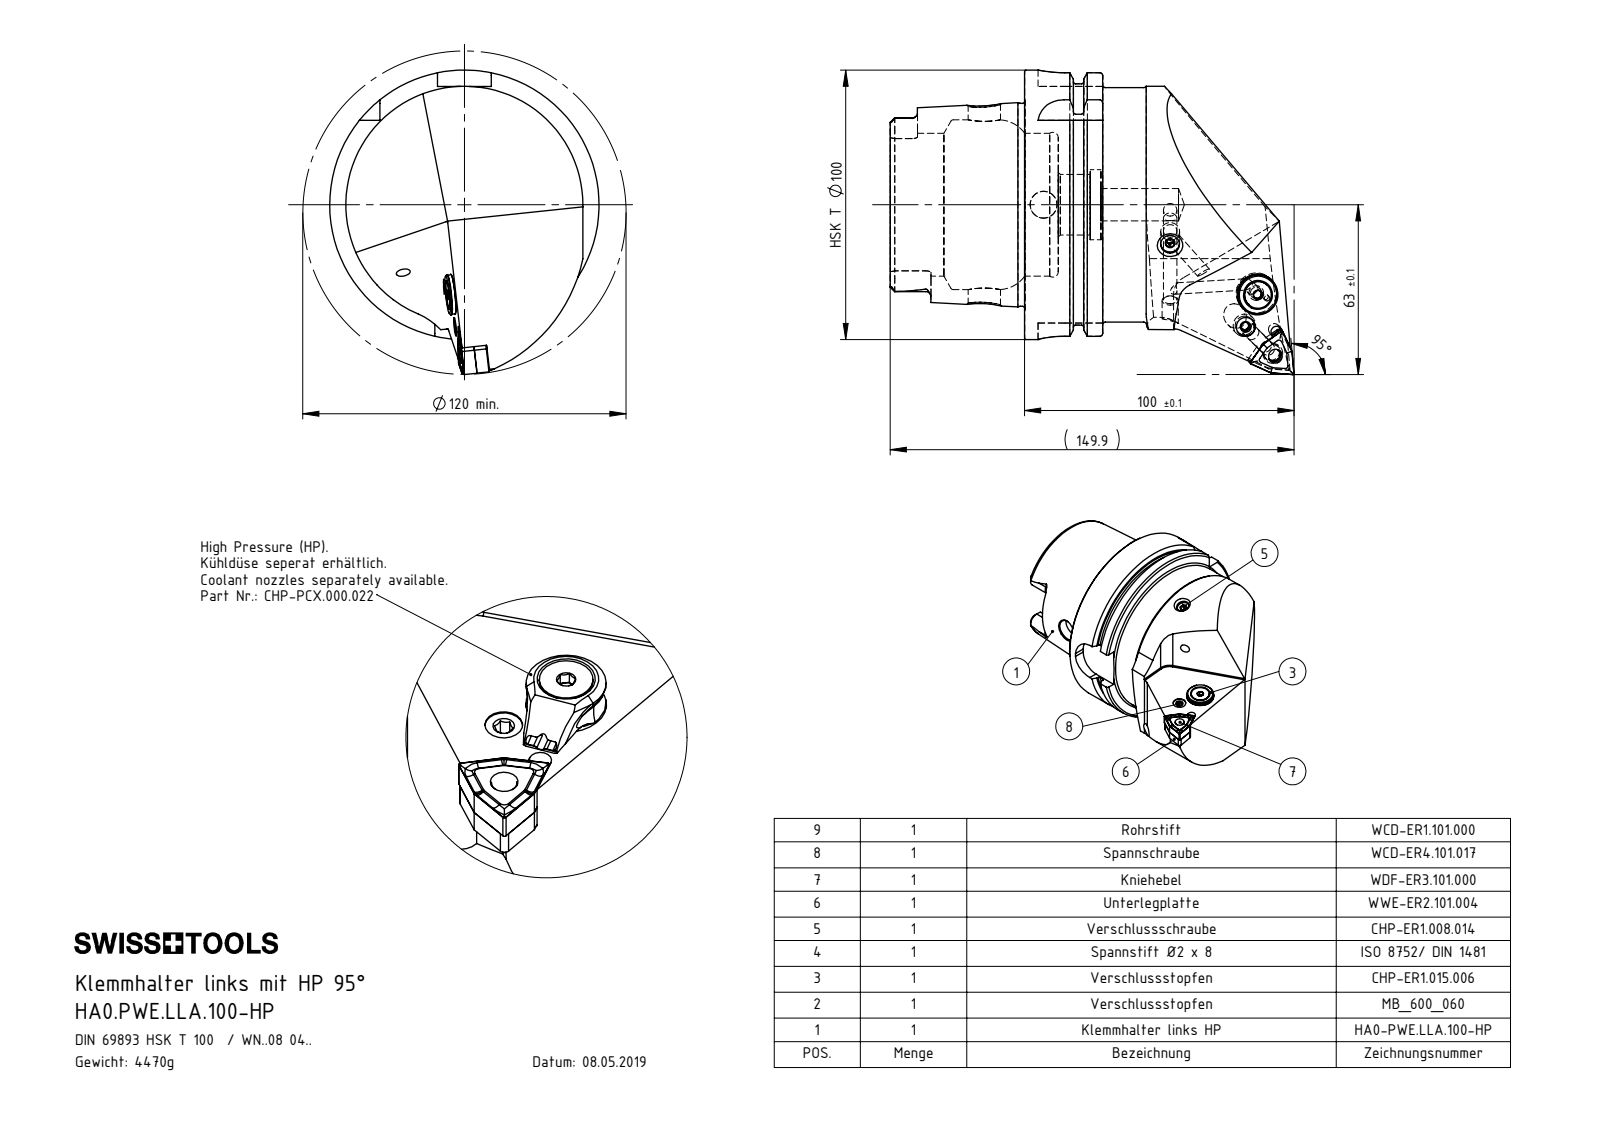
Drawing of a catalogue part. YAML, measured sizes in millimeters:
part_name: "WCD-ER4.101.017_A; WNMG080404; CHP-ER1.008.014_A; CHP-ER1.015.006_A (+8 more)"
step_written_by: "SolidWorks 2017 (AUTOMOTIVE_DESIGN)"
units: millimeters
bodies: {solids: 13, faces: 395, planar: 166, cylindrical: 91, other: 138}
overall_size: [149.9, 113, 100]
volume: 569262
surface_area: 75412
round_holes:
  - {diameter: 5, count: 4}
  - {diameter: 4.2, count: 2}
  - {diameter: 7, count: 2}
  - {diameter: 12, count: 2}
  - {diameter: 1.2, count: 1}
  - {diameter: 2, count: 1}
  - {diameter: 2.5, count: 1}
  - {diameter: 3, count: 1}
  - {diameter: 5.16, count: 1}
  - {diameter: 5.2, count: 1}
  - {diameter: 6, count: 1}
  - {diameter: 6.7, count: 1}
round_bosses_or_shafts:
  - {diameter: 8, count: 2}
  - {diameter: 100, count: 1}
  - {diameter: 91.95, count: 1}
  - {diameter: 87, count: 1}
  - {diameter: 75.26, count: 1}
  - {diameter: 15, count: 1}
  - {diameter: 13.4, count: 1}
  - {diameter: 10, count: 1}
partial_cylinders:
  - {radius: 1.9, count: 6}
  - {radius: 10, count: 4}
  - {radius: 0.4, count: 3}
  - {radius: 1, count: 3}
  - {radius: 2.5, count: 3}
  - {radius: 0.5, count: 2}
  - {radius: 4.83, count: 2}
  - {radius: 4.88, count: 2}
face_to_face_distances: [12.45, 28.95, 16.5, 49.9, 62.35, 78.85, 87.8, 78.2, 28.3, 15.85]
hole_center_spacings: [4.5, 12.84, 13.09, 21.26, 15.6, 24.05, 24.06]
